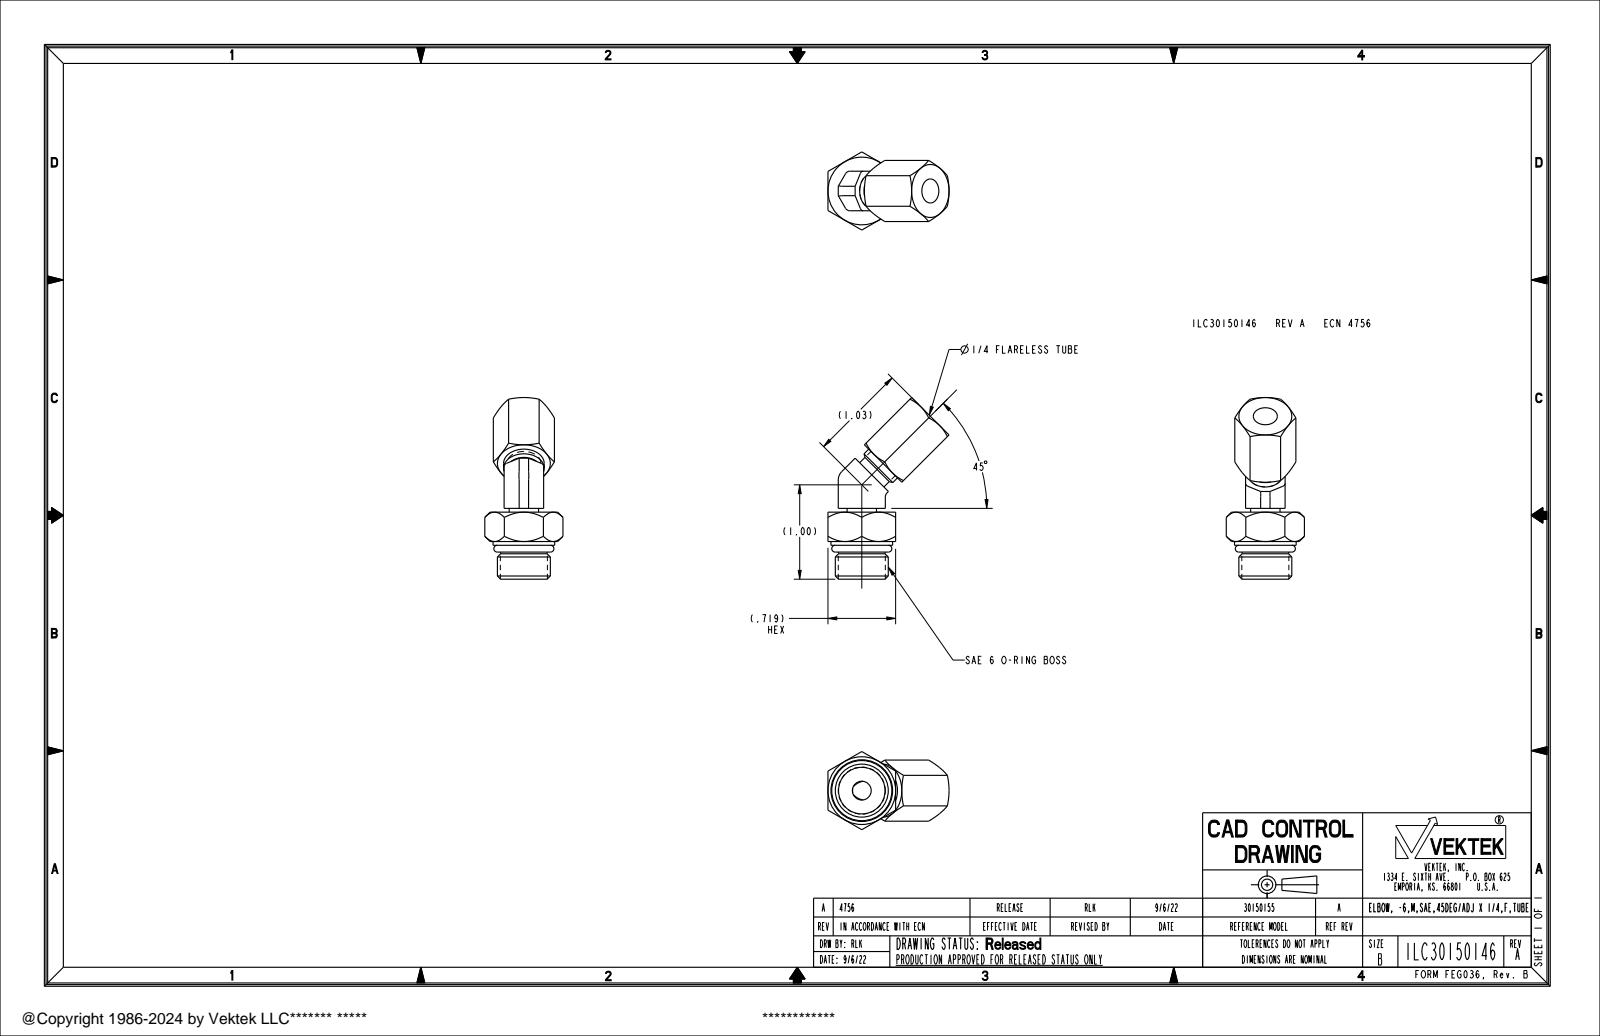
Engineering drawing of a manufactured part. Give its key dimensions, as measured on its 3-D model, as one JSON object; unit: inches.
{"part_name": "ILC30150146", "step_written_by": "CREO PARAMETRIC BY PTC INC, 2021164 (AUTOMOTIVE_DESIGN)", "units": "inches", "bodies": {"solids": 2, "faces": 115, "planar": 35, "cylindrical": 38, "other": 42}, "overall_size": [1.929, 1.287, 0.83], "volume_in3": 0.455, "surface_area_in2": 7.593, "round_holes": [[0.2, 2], [0.255, 1]], "round_bosses_or_shafts": [[0.655, 1], [0.563, 1], [0.5, 1], [0.494, 1], [0.432, 1], [0.364, 1], [0.312, 1]], "partial_cylinders_radius": [[0.05, 8], [0.06, 3], [0.125, 3]], "face_to_face_distances": [0.562, 0.719, 0.352, 0.04, 0.712, 0.36, 0.752, 0.392, 0.42, 0.71]}
